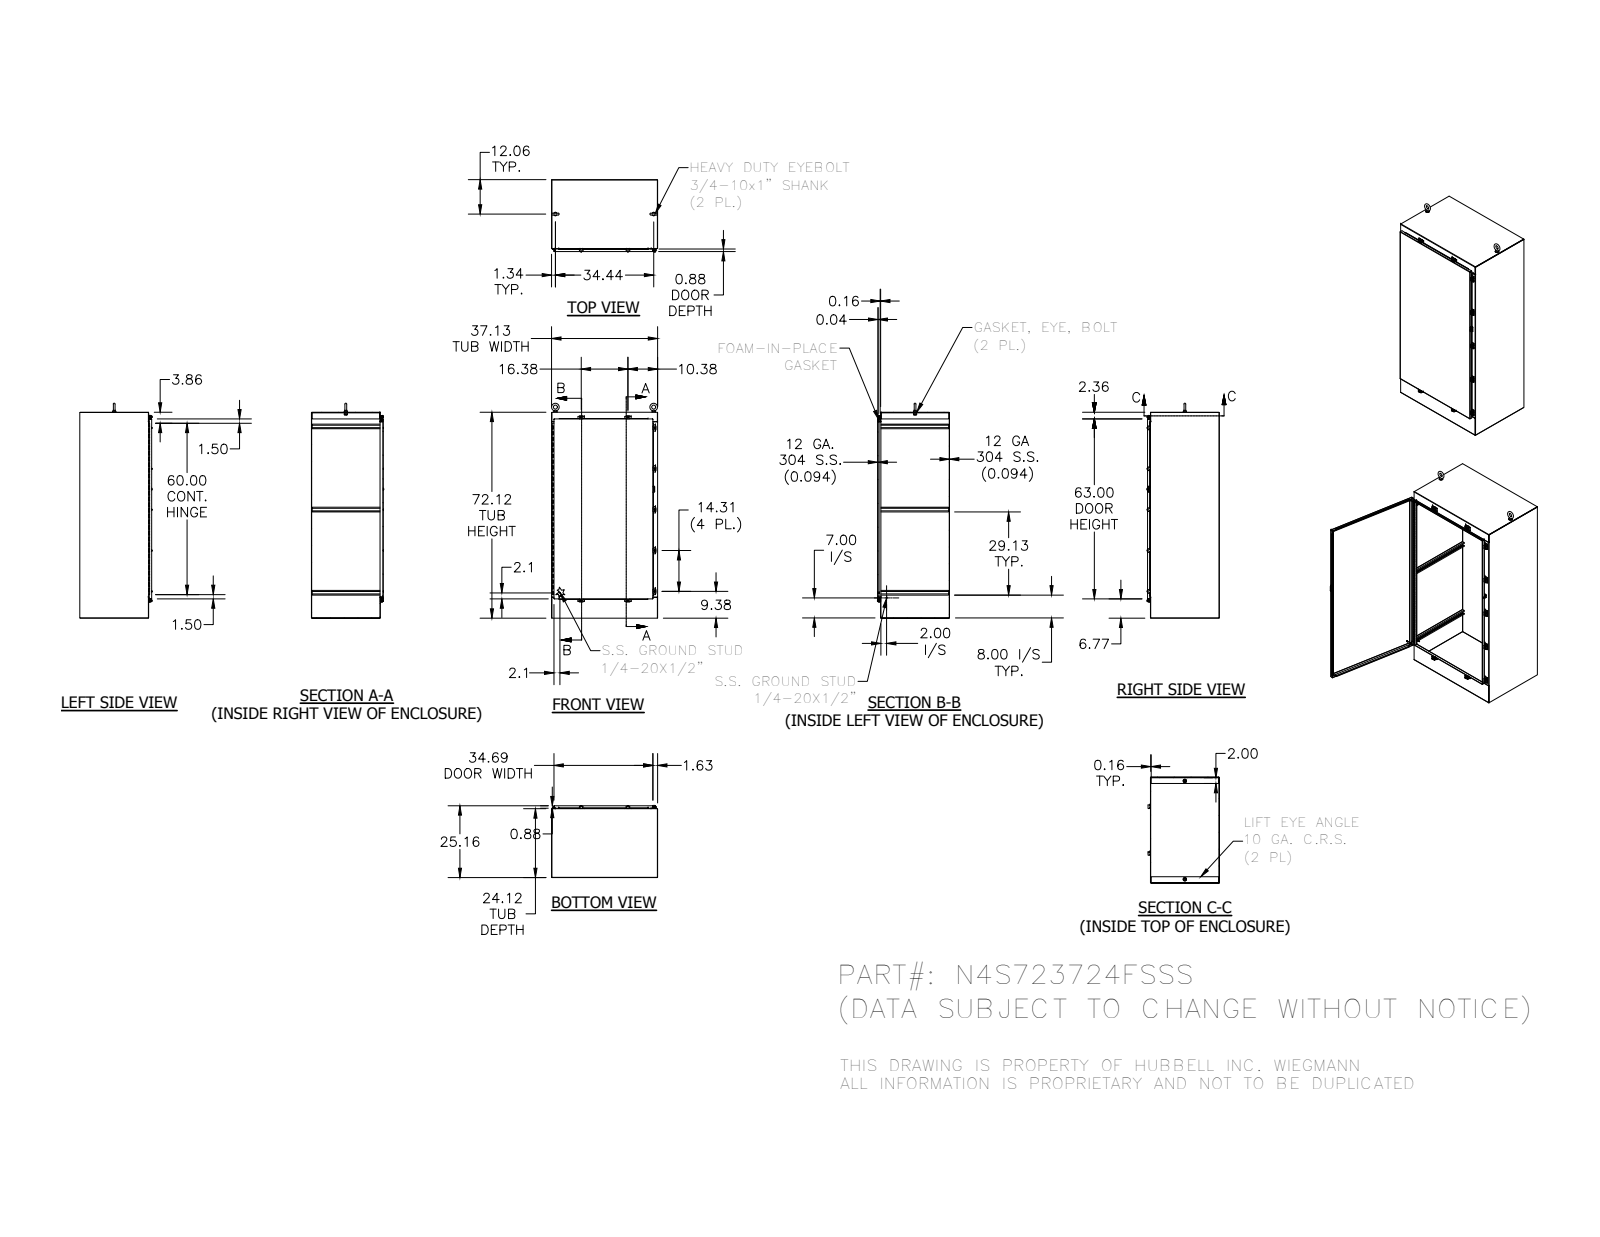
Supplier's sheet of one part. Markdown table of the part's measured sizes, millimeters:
| quantity | value |
| --- | --- |
| part name | FUN00103_1; HSSN1300W60L_1; 30824_1; 349132_1 (+8 more) |
| STEP written by | SolidWorks 2014 (AUTOMOTIVE_DESIGN) |
| units | millimeters |
| bodies | 78 solids, 3000 faces (1210 planar, 1210 cylindrical, 580 other) |
| overall size | 1911.3 × 943 × 644 |
| volume | 20 160 000 mm³ |
| surface area | 16 390 000 mm² |
| round holes (diameter × count) | 5.4 × 9, 7.1 × 9, 7.6 × 9, 2.8 × 3, 16.3 × 2, 20.7 × 2, 3.2 × 1, 4 × 1, 12.7 × 1 |
| round bosses / shafts (diameter × count) | 6.4 × 12, 13.2 × 9, 12.7 × 9, 8.9 × 9, 31.8 × 2, 28.4 × 2, 19.1 × 2, 8.6 × 2 |
| partial cylindrical surfaces (radius × count) | 0.8 × 107, 3.2 × 43, 1.6 × 22, 6.4 × 21, 0.8 × 19, 0.5 × 18, 1.3 × 18, 2.2 × 18 |
| main face-to-face distances | 2.4, 636.7, 940.6, 634.3, 639.1, 938.2, 1829.6, 943, 610.4, 26.3 |
| hole center spacings | 363.6, 727.1, 20, 416.1, 1090.7, 1635.1, 1687.2, 11.4 |
